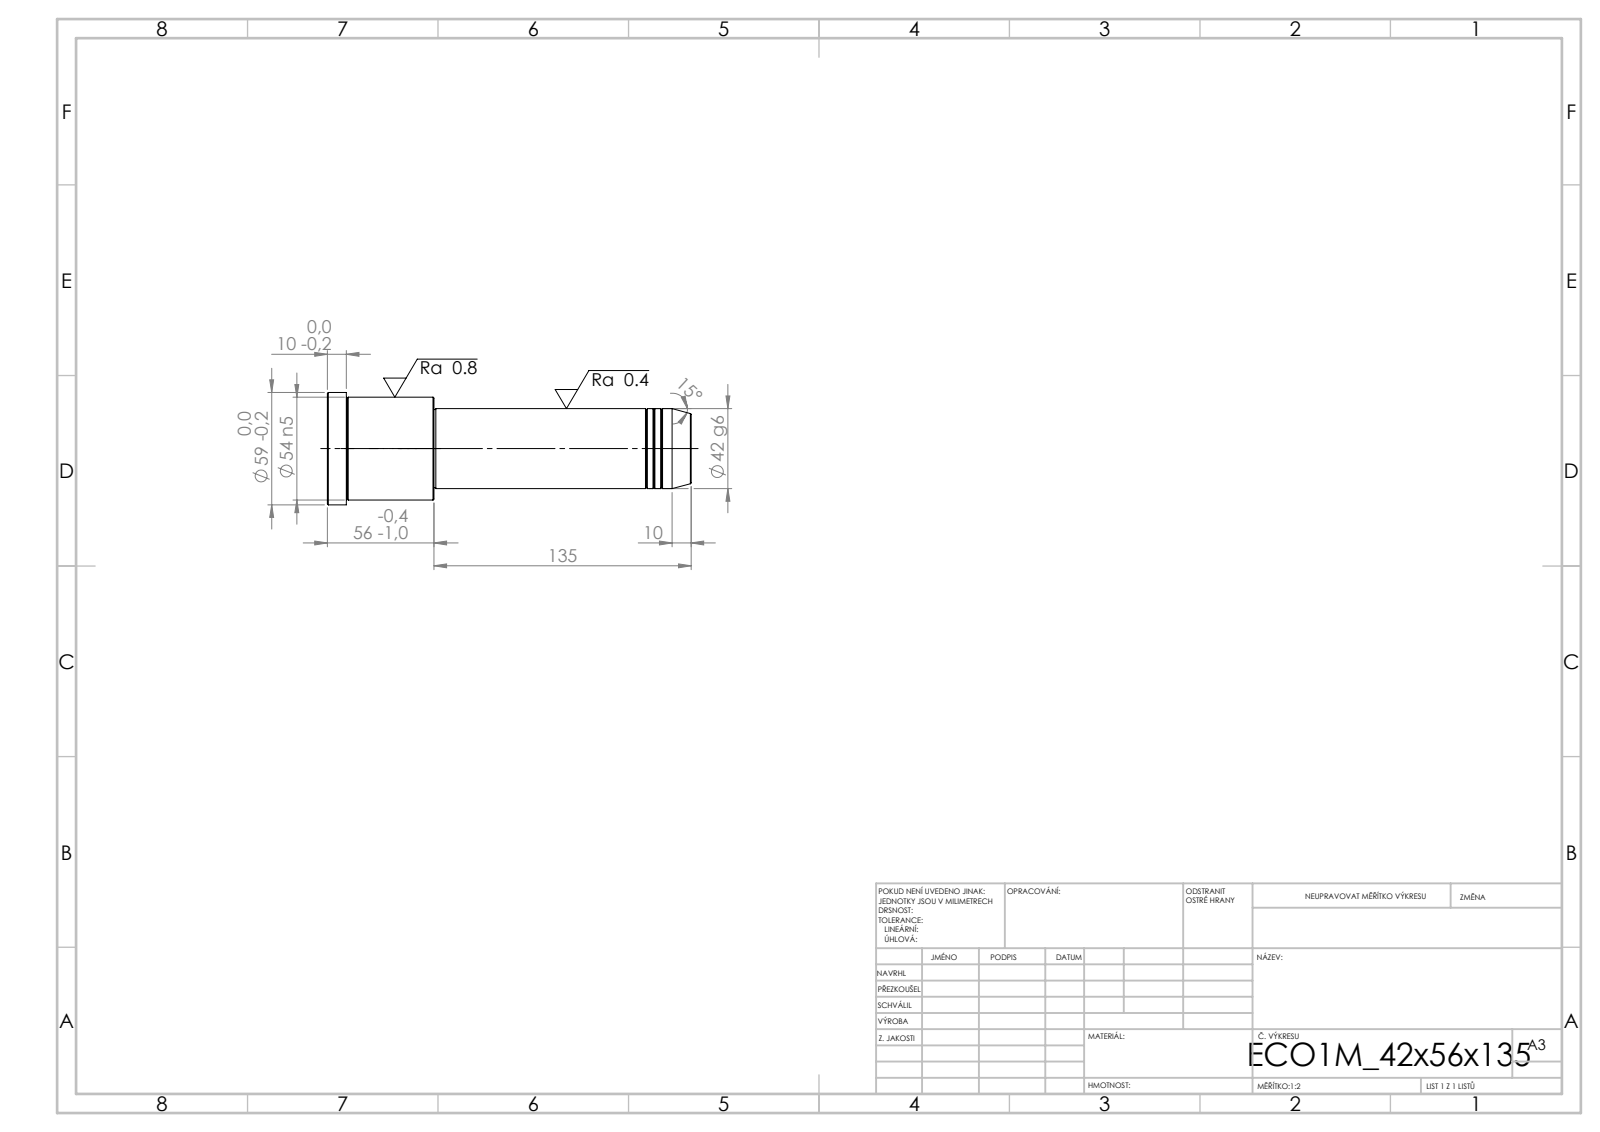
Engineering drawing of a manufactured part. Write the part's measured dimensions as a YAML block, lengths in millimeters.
step_written_by: "SolidWorks 2019 (CONFIG_CONTROL_DESIGN)"
units: millimeters
bodies: {solids: 1, faces: 43, planar: 5, cylindrical: 14, other: 24}
overall_size: [191, 59, 59]
volume: 317700
surface_area: 32886
round_bosses_or_shafts:
  - {diameter: 59, count: 1}
  - {diameter: 54, count: 1}
  - {diameter: 42, count: 1}
  - {diameter: 41, count: 1}
face_to_face_distances: [191, 135, 56, 181, 46, 10, 134, 1, 47, 57]
